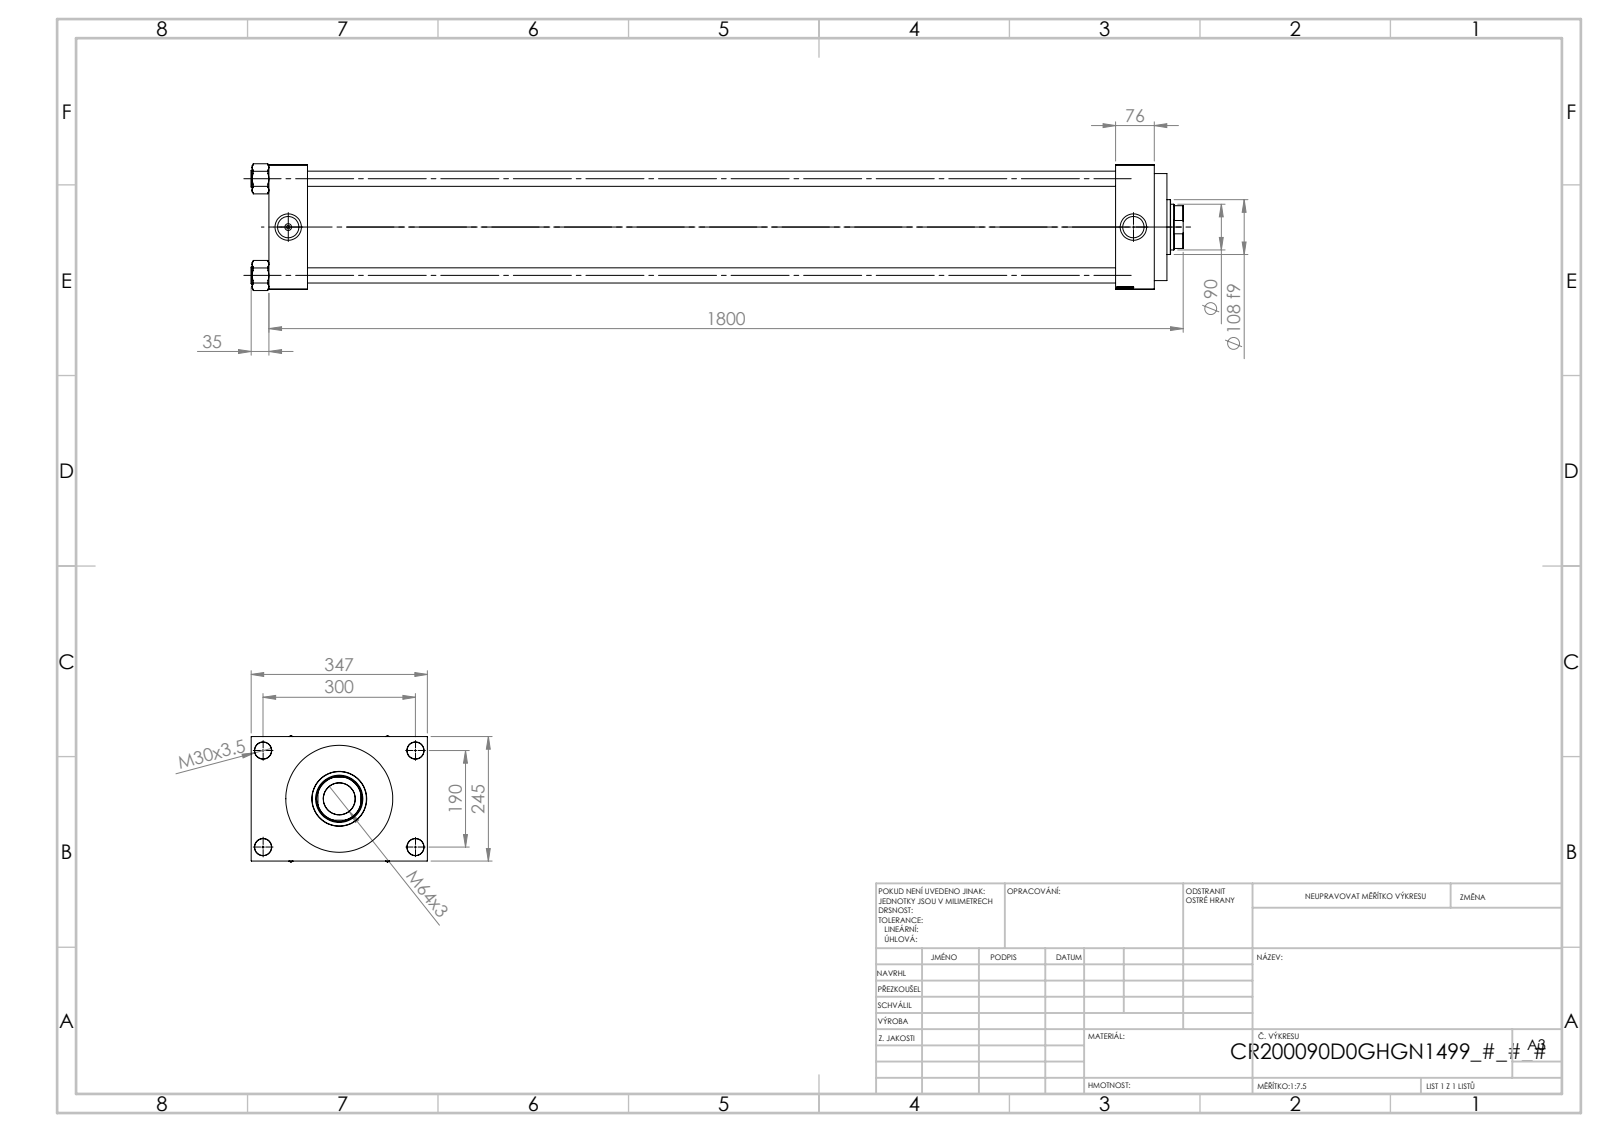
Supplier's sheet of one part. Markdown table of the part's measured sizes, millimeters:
| quantity | value |
| --- | --- |
| part name | V215CR_D_Body; NUT_M5_D; V215CR_VCP_D; V215CR_D_TYCINKA (+1 more) |
| STEP written by | SolidWorks 2019 (CONFIG_CONTROL_DESIGN) |
| units | millimeters |
| bodies | 11 solids, 1148 faces (544 planar, 86 cylindrical, 518 other) |
| overall size | 1835 × 347 × 249.44 |
| volume | 31 070 000 mm³ |
| surface area | 3 959 000 mm² |
| round holes (diameter × count) | 30 × 4, 33 × 4, 7 × 2, 41.92 × 2, 52 × 2, 62.5 × 1, 90 × 1, 93 × 1, 146 × 1, 200 × 1, 210.5 × 1 |
| round bosses / shafts (diameter × count) | 33 × 4, 206 × 1, 108 × 1 |
| partial cylindrical surfaces (radius × count) | 44 × 1 |
| main face-to-face distances | 76, 1667, 245, 1591, 1743, 1724.74, 1648.74, 57.74, 18.26, 51 |
| hole center spacings | 54.9, 134.49, 177.55, 190.2, 197.87, 245.1, 310.18, 190 |
